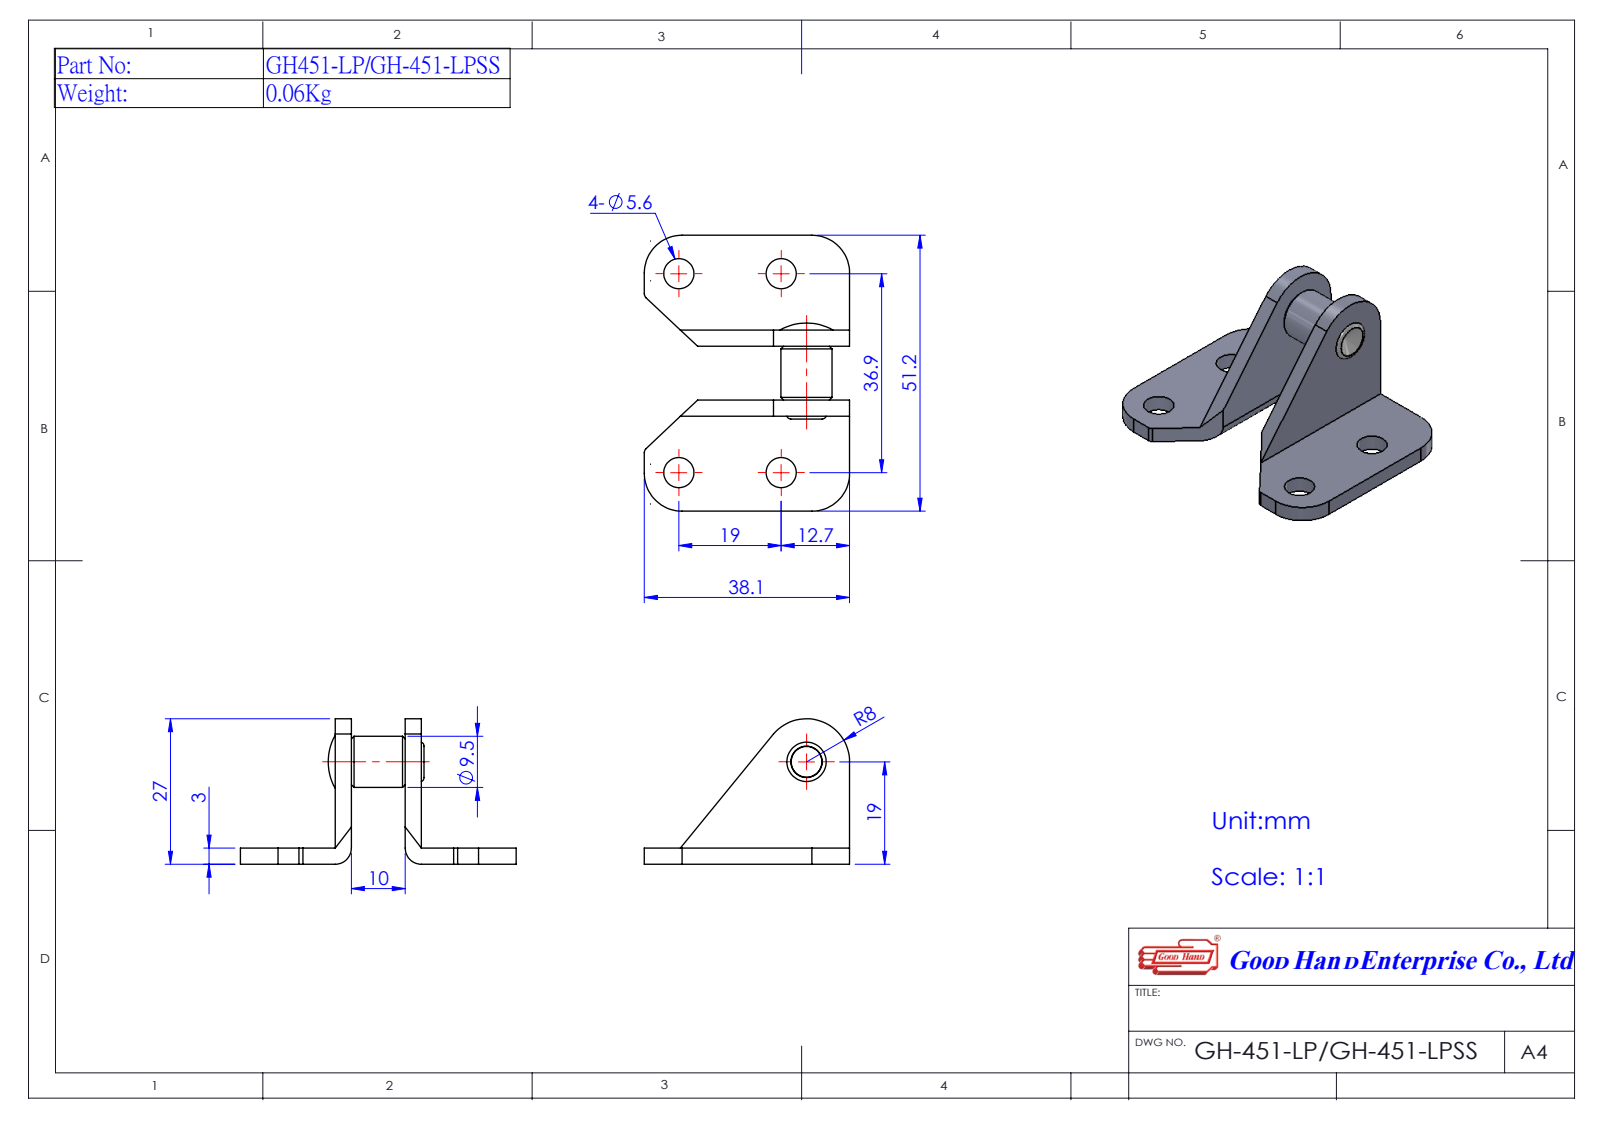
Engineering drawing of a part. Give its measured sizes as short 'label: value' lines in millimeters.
name: GH-451-LPSS(簡化); Group1^GH-451-LP(簡化)
written by: SolidWorks 2016 (AUTOMOTIVE_DESIGN)
unit: mm
bodies: 1 solid, 52 faces (22 planar, 24 cylindrical, 6 other)
size: 51.2 × 38.1 × 27
volume: 7 654 mm³; area: 6 213 mm²
holes: 4× ⌀5.6, 1× ⌀6.5
bosses: 1× ⌀9.5, 1× ⌀6.33
rounds: 4× R7, 2× R1, 2× R3, 1× R8
face distances: 3, 13, 10, 16, 17.6, 20.6, 30.6, 33.6, 51.2, 38.1
hole spacings: 19, 36.9, 41.5
